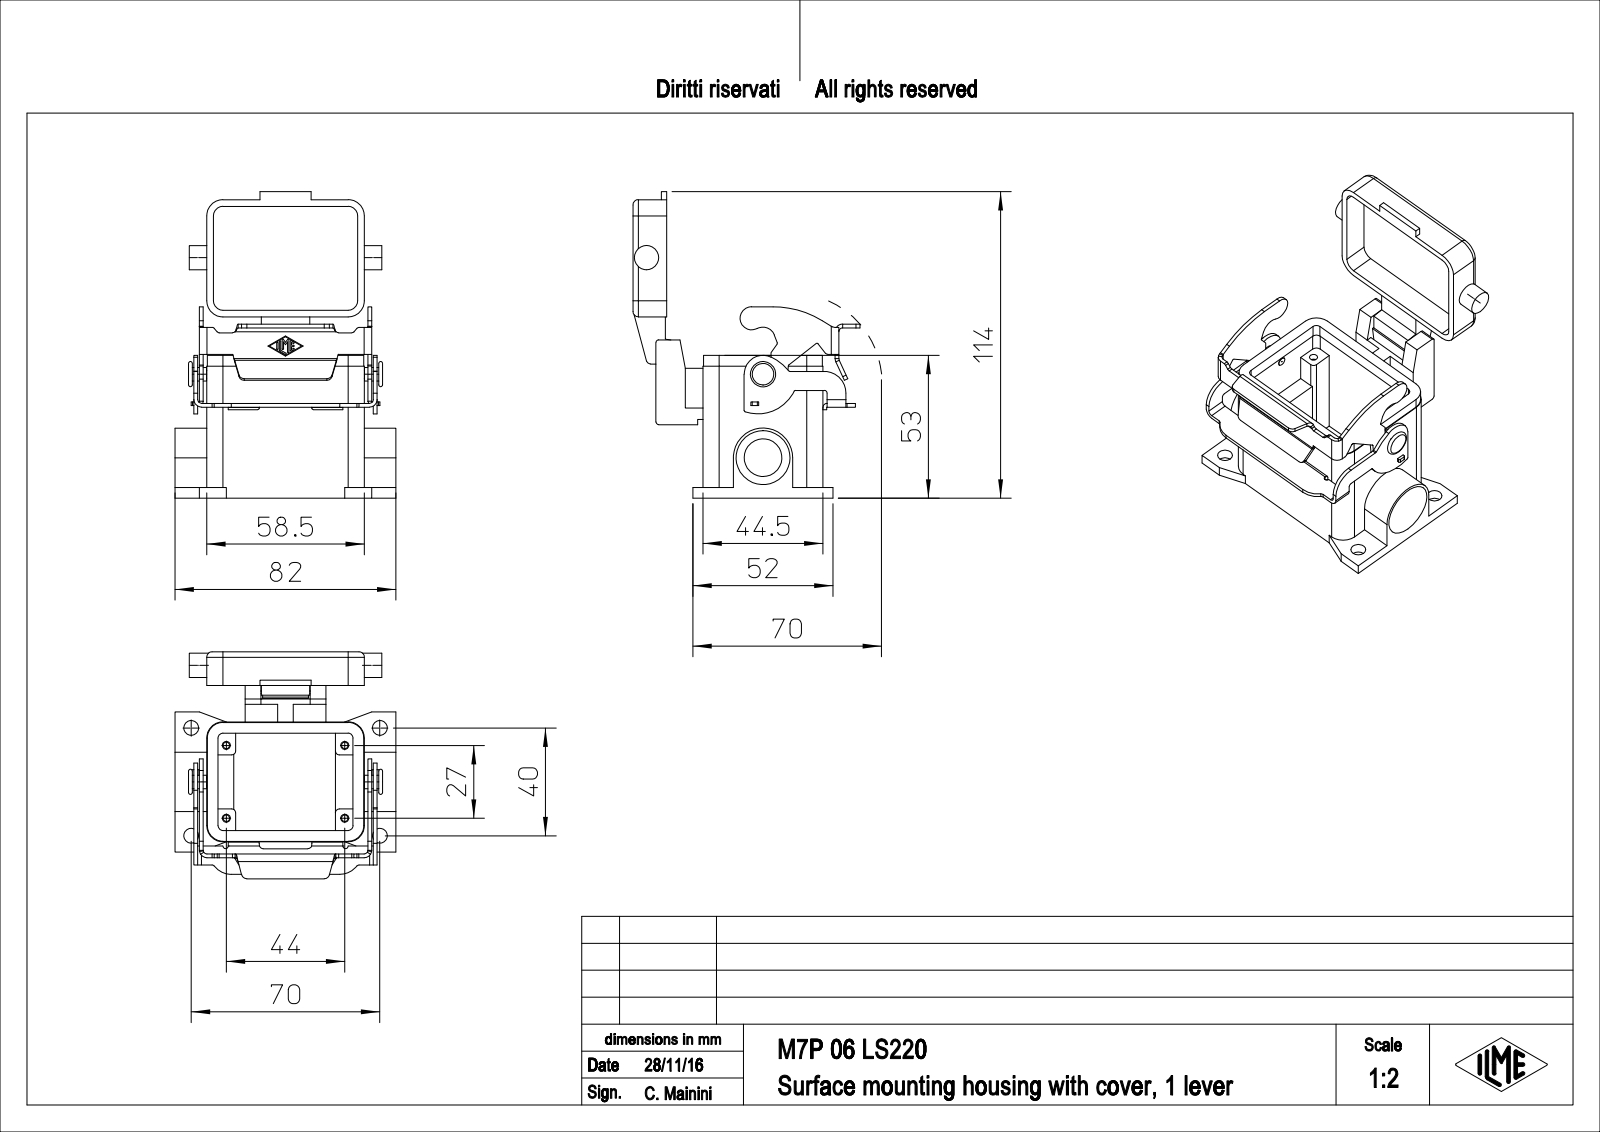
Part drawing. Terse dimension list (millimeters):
name: M7P_06_LS220
written by: PTC Creo Elements/Direct Modeling 19.0E 27-Jun-2016 (C) Parametric Technology GmbH (AUTOMOTIVE_DESIGN)
unit: mm
bodies: 1 solid, 505 faces (277 planar, 200 cylindrical, 28 other)
size: 113.75 × 84.23 × 82
volume: 94 976 mm³; area: 53 099 mm²
holes: 4× ⌀2.46, 4× ⌀3, 4× ⌀5.5, 1× ⌀14, 1× ⌀20
bosses: 1× ⌀9, 1× ⌀7, 1× ⌀5, 1× ⌀4, 1× ⌀3.2, 1× ⌀3
rounds: 16× R0.25, 14× R1, 12× R0.5, 12× R1.5, 12× R2, 8× R6, 6× R1.4, 6× R2.8
face distances: 4, 1.4, 40.5, 3.5, 26, 22.5, 44.5, 30, 70.5, 67
hole spacings: 14.53, 35.93, 57.37, 66.12, 27, 40, 44, 51.62
